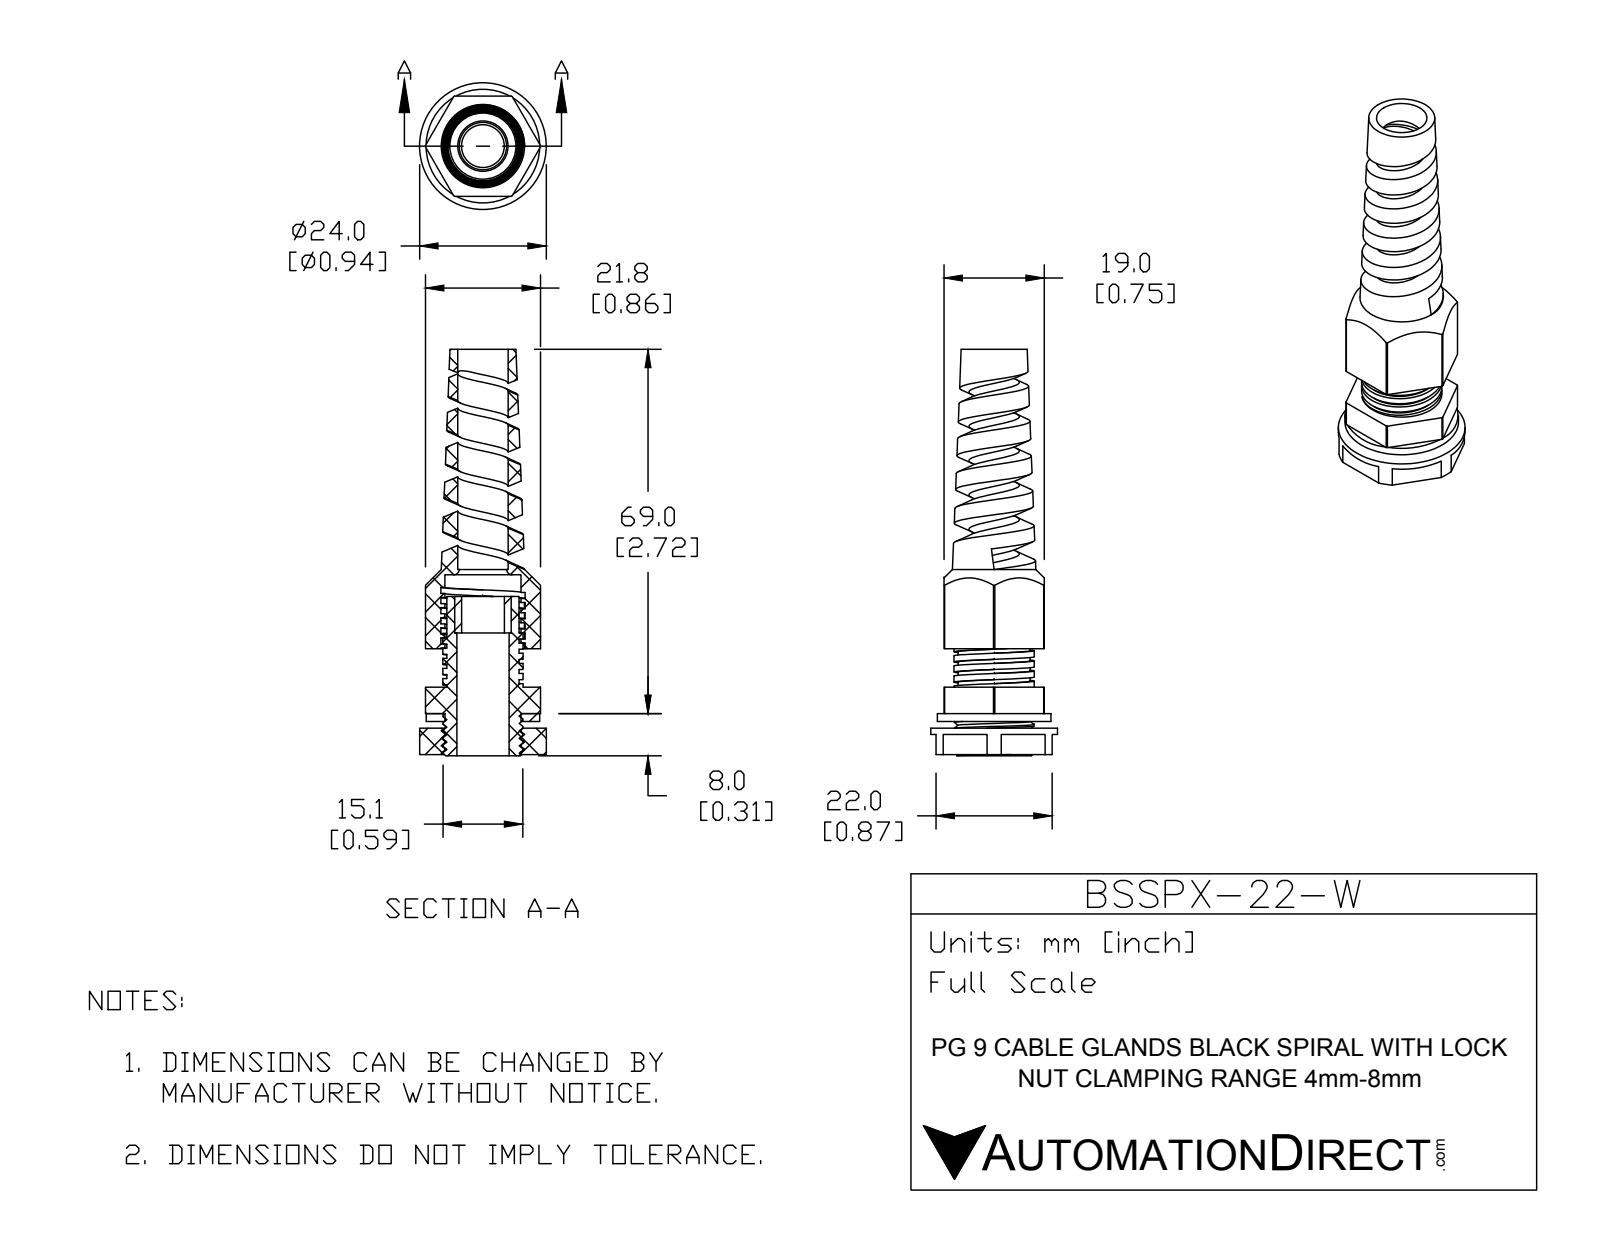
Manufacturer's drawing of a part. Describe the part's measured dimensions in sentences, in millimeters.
The part is named "BSSPX-22-W". Its 3-D file was written by "SolidWorks 2015 (CONFIG_CONTROL_DESIGN)". It is 5 solids with 226 faces: 103 planar, 89 cylindrical and 34 other. Overall it measures 77 by 24 by 24 millimeters. Its volume is 9 298 cubic millimeters and its surface area 11 398 square millimeters. Round holes: 1 of diameter 8.11, 1 of diameter 9.55, 1 of diameter 9.9, 1 of diameter 10.71, 1 of diameter 14.4, 1 of diameter 14.43, 1 of diameter 14.44. Round bosses or shafts: 1 of diameter 24, 1 of diameter 21.51, 1 of diameter 15.2, 1 of diameter 15.1, 1 of diameter 13.7. Partial cylindrical surfaces (rounded edges, fillets, slot ends): 1 of radius 10.9. The main face-to-face distances are 19, 1.5, 5, 7.5, 2.5, 6.5, 20.5, 1, 6, 0.5.
